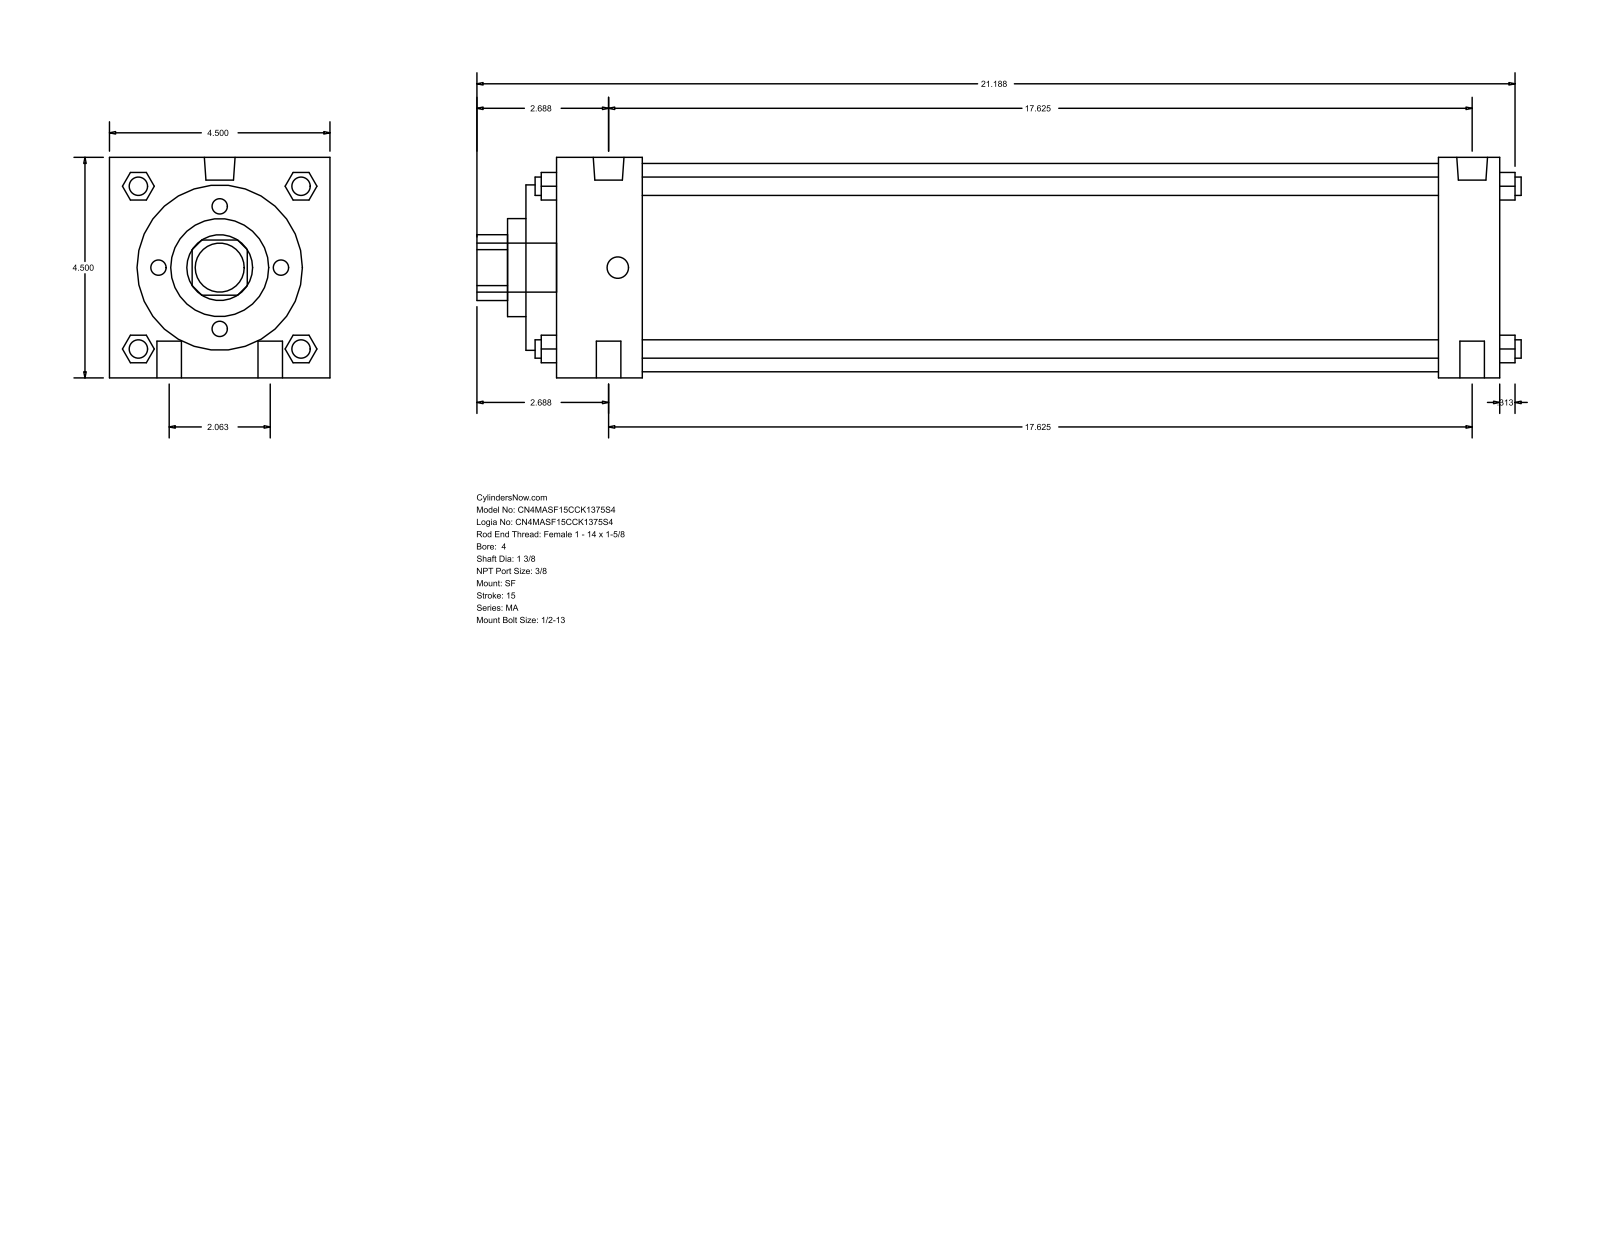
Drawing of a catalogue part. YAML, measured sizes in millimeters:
part_name: "MA_SF__0400_1.375"
step_written_by: "GSSL Pune (CONFIG_CONTROL_DESIGN)"
units: millimeters
bodies: {solids: 0, faces: 126, planar: 95, cylindrical: 31, other: 0}
overall_size: [541.34, 114.3, 114.3]
round_holes:
  - {diameter: 34.92, count: 1}
  - {diameter: 50.8, count: 1}
  - {diameter: 85.72, count: 1}
  - {diameter: 107.95, count: 1}
round_bosses_or_shafts:
  - {diameter: 12.7, count: 4}
  - {diameter: 9.53, count: 4}
  - {diameter: 15.93, count: 2}
  - {diameter: 11.11, count: 2}
  - {diameter: 25.4, count: 1}
partial_cylinders:
  - {radius: 17.06, count: 1}
face_to_face_distances: [114.3, 488.96, 15.87, 504.83, 473.08, 457.21, 31.75, 60.32, 44.45, 412.76]
